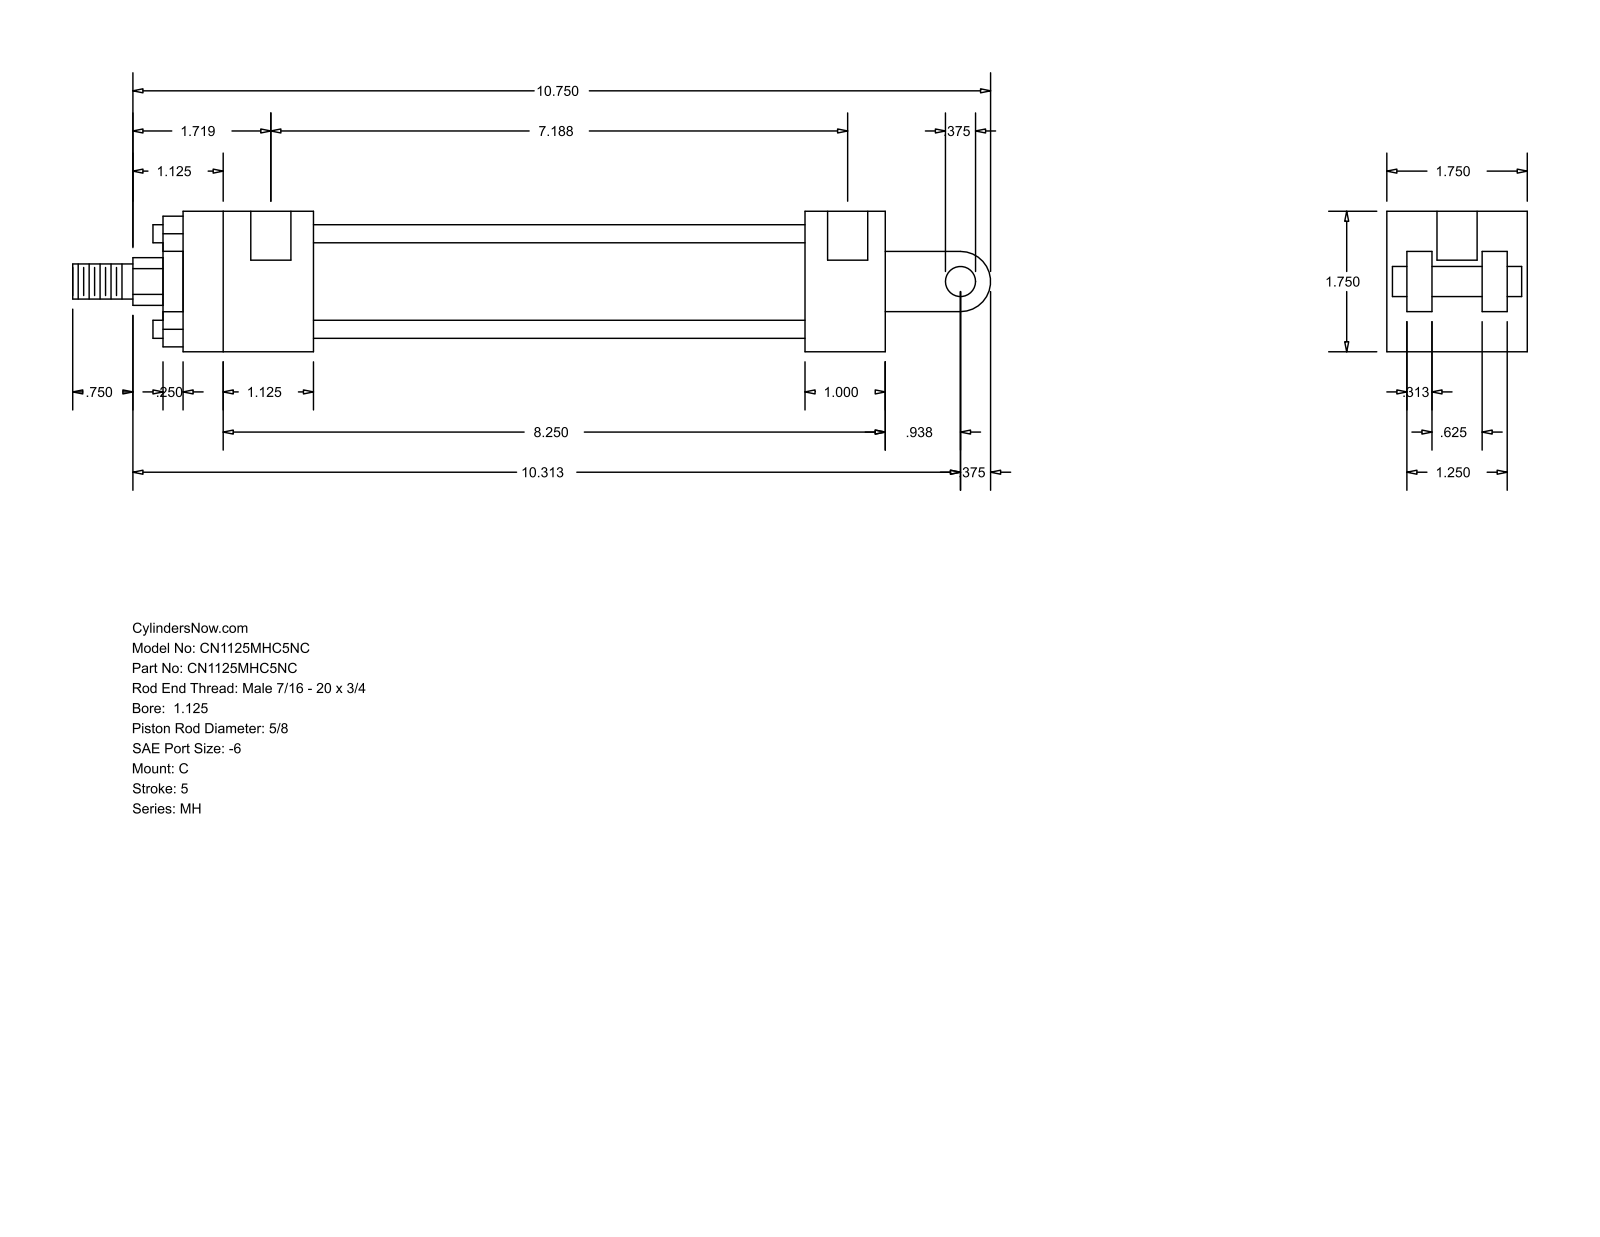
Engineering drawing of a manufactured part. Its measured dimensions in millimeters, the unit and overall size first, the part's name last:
Units: millimetres
Overall size (bounding box): 290.51 × 44.45 × 44.45
Round holes (diameter × count): ⌀5.56 ×4, ⌀12.7 ×2
Round bosses / shafts (diameter × count): ⌀5.71 ×4, ⌀34.92 ×1, ⌀28.57 ×1, ⌀15.88 ×1, ⌀11.11 ×1, ⌀9.53 ×1
Partial cylindrical surfaces — rounded edges, fillets, slot ends (radius × count): R7.54 ×1, R9.53 ×1
Main face-to-face distances: 44.46, 6.35, 31.76, 14.29, 25.4, 30.17, 38.11, 7.94, 23.82, 41.27
Hole centre spacings: 179.39, 3.17, 182.56
Bodies: 0 solids, 99 faces (70 planar, 29 cylindrical, 0 other)
Part name (STEP PRODUCT): MH_C__0112_0.625
STEP written by: GSSL Pune (CONFIG_CONTROL_DESIGN)
